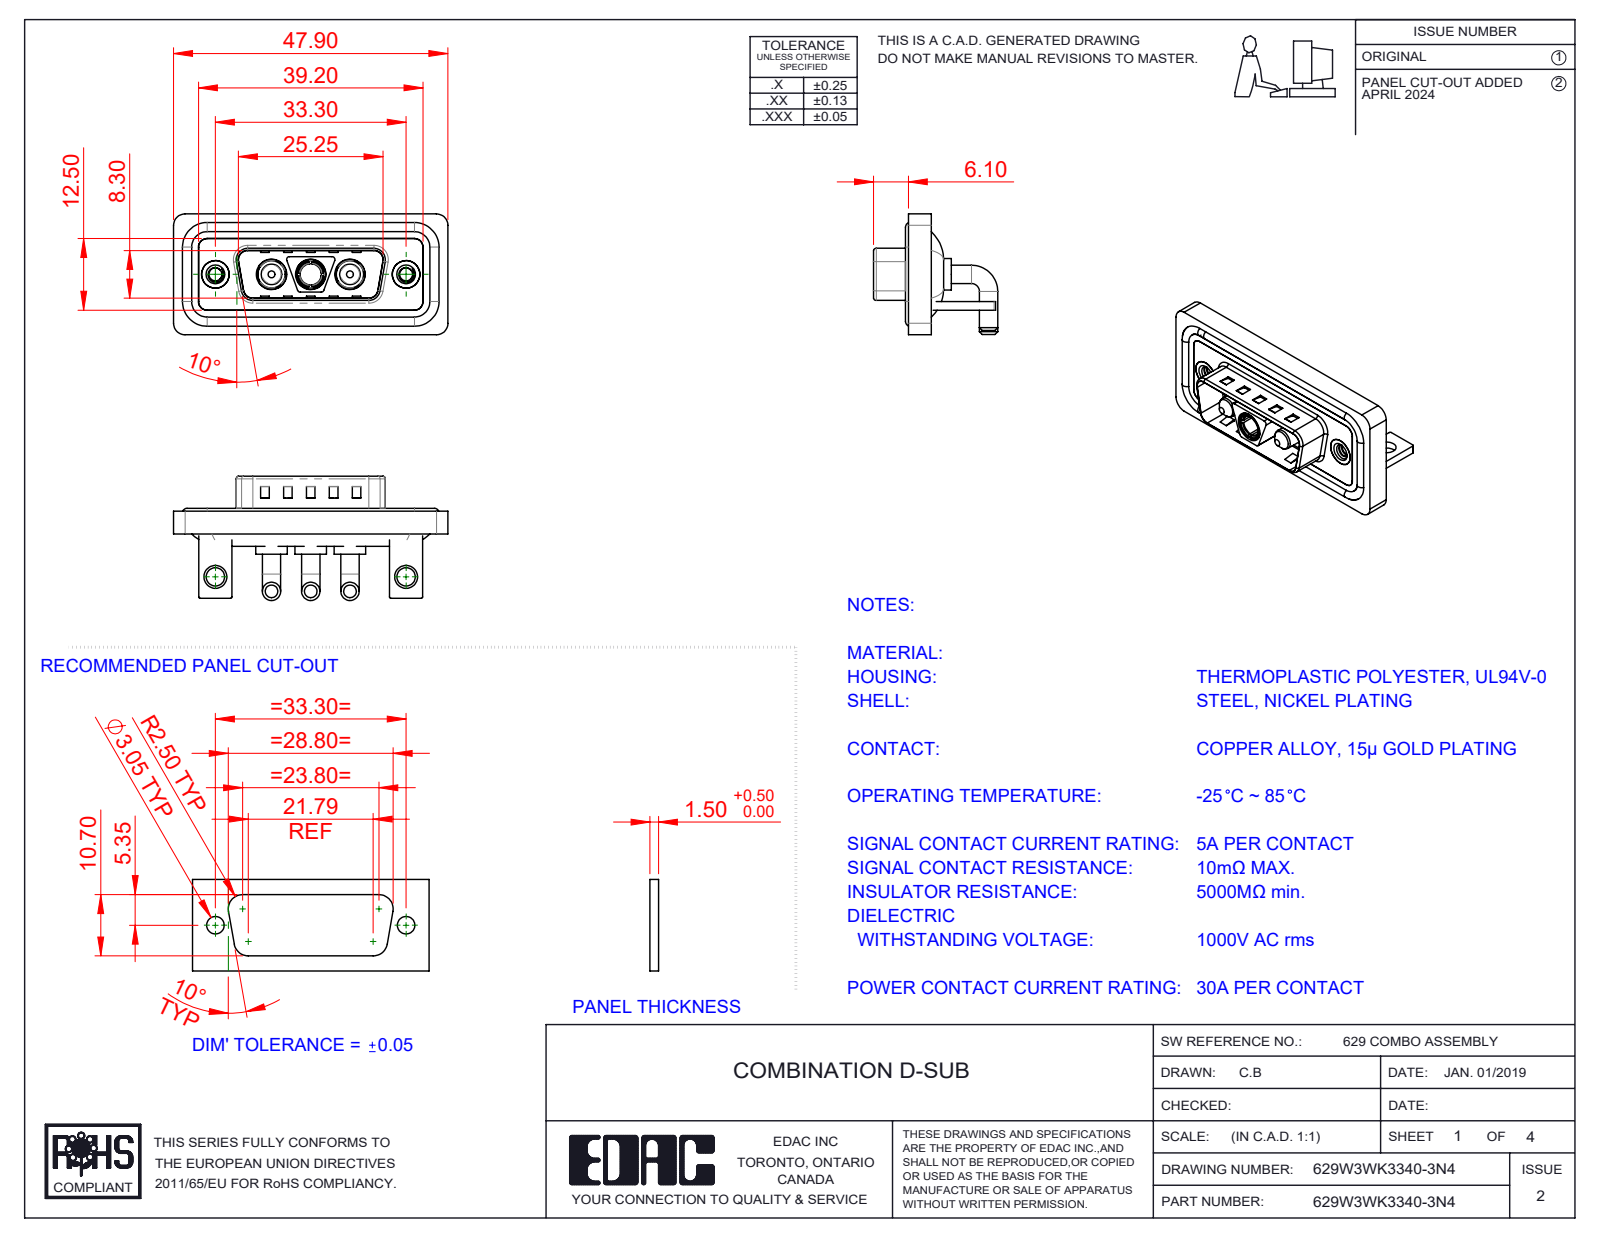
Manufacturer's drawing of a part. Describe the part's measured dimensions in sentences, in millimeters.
The part is named "629Combo Threaded Rivet_3; Power Pin_30A RA; 629Combo Shell Rear_15 Contacts; 629Combo Stabilizer Bracket (+5 more)". Its 3-D file was written by "SolidWorks 2023 (CONFIG_CONTROL_DESIGN)". It is 15 solids with 661 faces: 251 planar, 274 cylindrical and 136 other. Overall it measures 47.9 by 21.7 by 21.1 millimeters. Its volume is 6 248 cubic millimeters and its surface area 10 059 square millimeters. Round holes: 3 of diameter 4.85, 3 of diameter 5.3, 2 of diameter 2.26, 2 of diameter 3.2, 2 of diameter 4, 2 of diameter 4.8, 2 of diameter 5, 1 of diameter 3.7. Round bosses or shafts: 6 of diameter 3.2, 4 of diameter 1.6, 3 of diameter 5.5, 3 of diameter 5.2, 3 of diameter 4.75, 3 of diameter 3.75, 2 of diameter 4.9, 2 of diameter 3.6. Partial cylindrical surfaces (rounded edges, fillets, slot ends): 21 of radius 2, 18 of radius 1.5, 16 of radius 0.25, 13 of radius 0.5, 8 of radius 1.6, 4 of radius 0.6, 4 of radius 0.65, 4 of radius 0.9. The main face-to-face distances are 0.4, 1.5, 0.8, 2.9, 1.1, 2.1, 3.7, 1.6, 1.2, 4.5. The hole center spacings are 6.85, 9.8, 16.65, 23.5, 33.3, 13.7.
